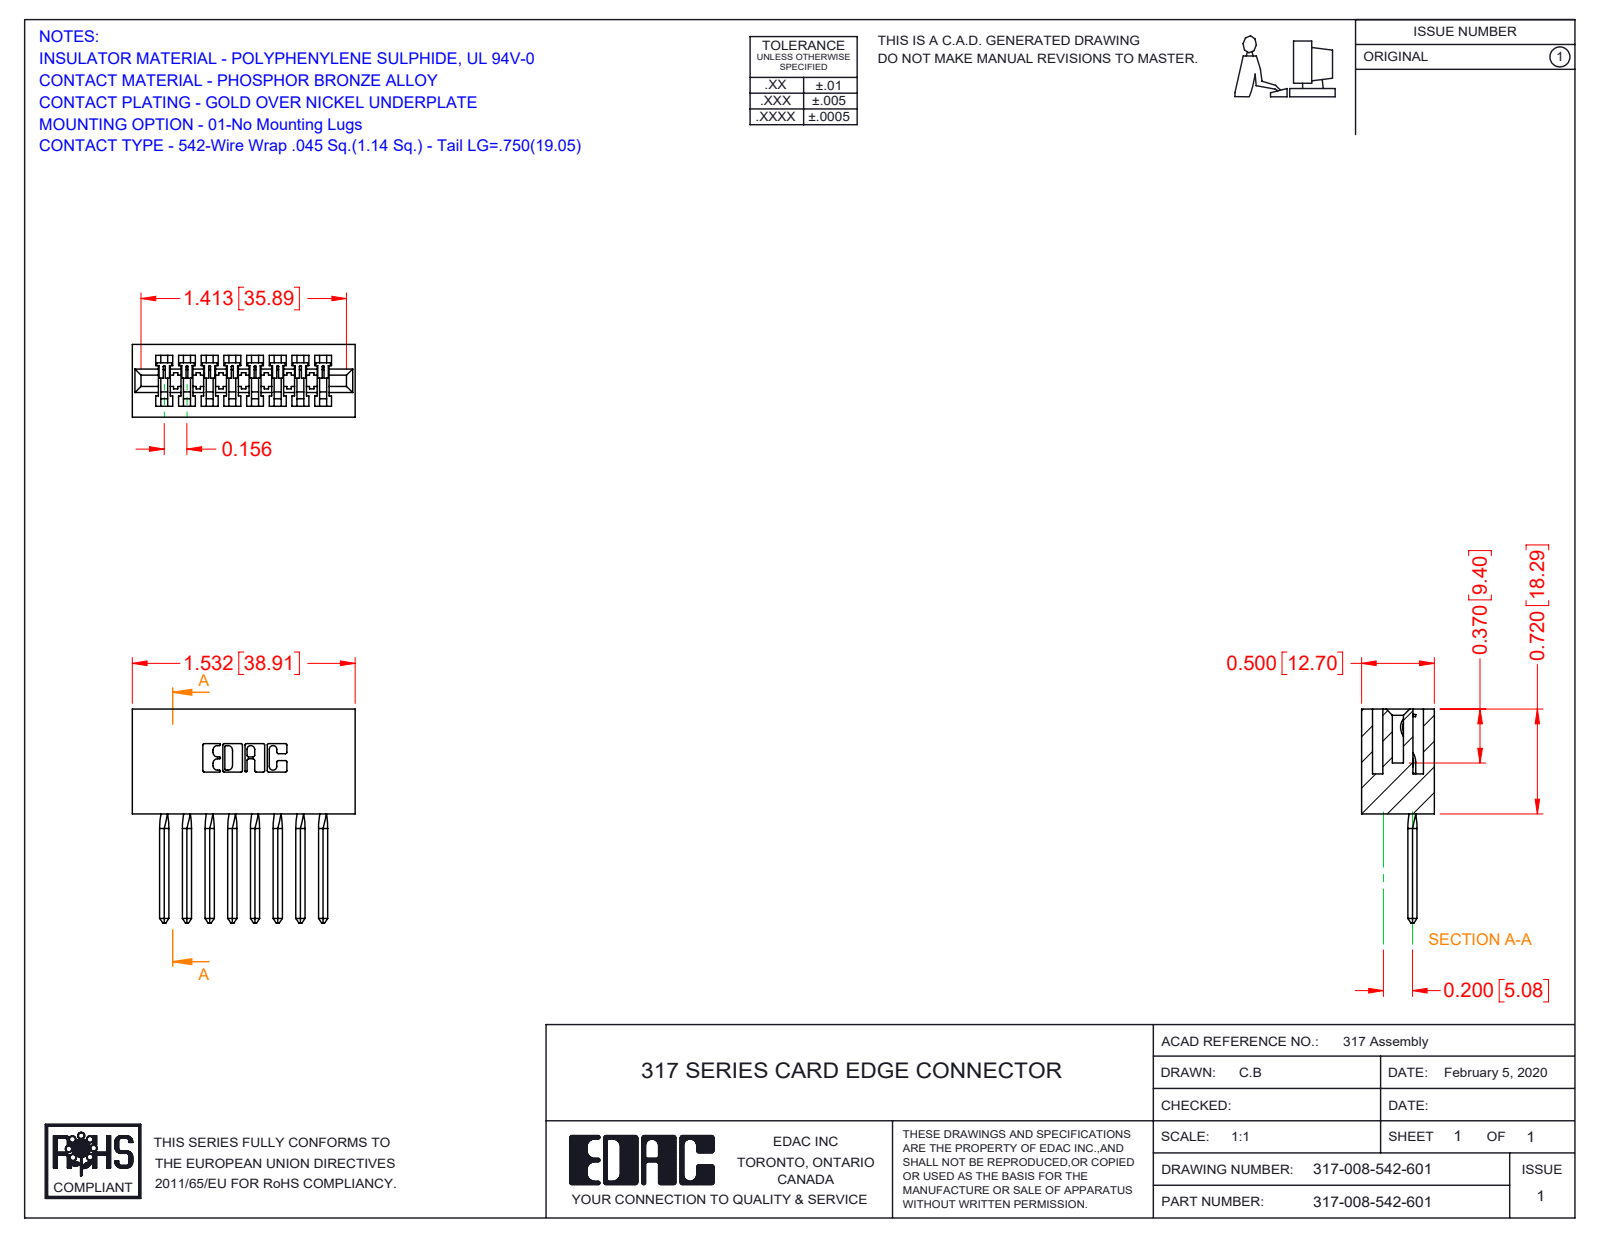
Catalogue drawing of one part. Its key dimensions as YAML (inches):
part_name: "317-290-003_542; 317-008-542-601; 317 Part_Lugless"
step_written_by: "SolidWorks 2016 (CONFIG_CONTROL_DESIGN)"
units: inches
bodies: {solids: 9, faces: 690, planar: 562, cylindrical: 96, other: 32}
overall_size: [1.532, 1.47, 0.5]
volume: 0.408
surface_area: 11.54
partial_cylinders:
  - {radius: 0.01, count: 22}
  - {radius: 0.006, count: 16}
  - {radius: 0.007, count: 6}
  - {radius: 0.031, count: 6}
  - {radius: 0.026, count: 3}
  - {radius: 0.074, count: 1}
  - {radius: 0.089, count: 1}
  - {radius: 0.1, count: 1}
face_to_face_distances: [0.5, 0.075, 0.425, 0.11, 0.156, 0.065, 0.116, 0.22, 0.624, 0.35]
